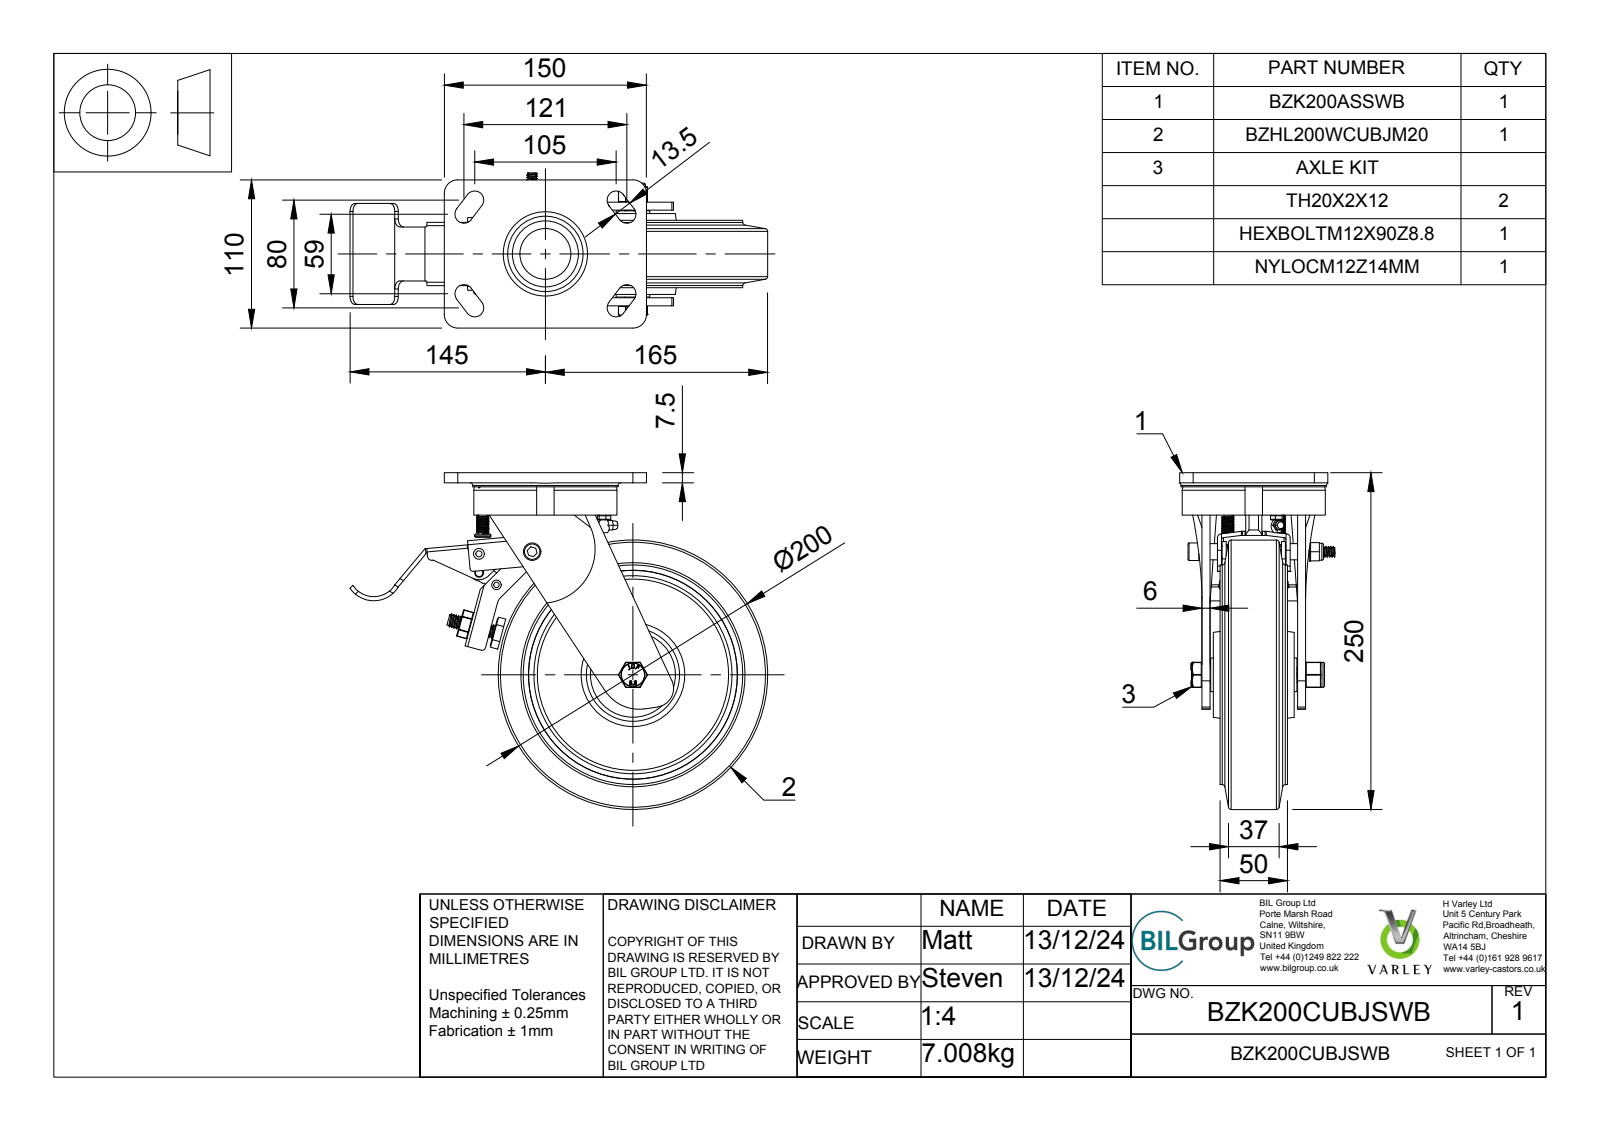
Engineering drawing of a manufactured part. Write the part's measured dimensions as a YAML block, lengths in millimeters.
part_name: "BZK200CUBJSWB v3; BZK200ASSWB v1; FABRICATED STEEL TOP PLATE; FABRICATED STEEL FORKS (+8 more)"
step_written_by: "Autodesk Translation Framework v13.20.0.188 (AP242_MANAGED_MODEL_BASED_3D_ENGINEERING_MIM_LF)"
units: millimeters
bodies: {solids: 56, faces: 1428, planar: 593, cylindrical: 366, other: 469}
overall_size: [310, 250, 115.22]
volume: 1364000
surface_area: 390820
round_holes:
  - {diameter: 6, count: 5}
  - {diameter: 10, count: 2}
  - {diameter: 5, count: 1}
  - {diameter: 8, count: 1}
  - {diameter: 12, count: 1}
  - {diameter: 12.2, count: 1}
  - {diameter: 13, count: 1}
  - {diameter: 14, count: 1}
  - {diameter: 20, count: 1}
  - {diameter: 28.5, count: 1}
  - {diameter: 30.8, count: 1}
  - {diameter: 37, count: 1}
round_bosses_or_shafts:
  - {diameter: 12, count: 3}
  - {diameter: 8, count: 2}
  - {diameter: 200, count: 1}
  - {diameter: 163, count: 1}
  - {diameter: 108, count: 1}
  - {diameter: 107, count: 1}
  - {diameter: 40.8, count: 1}
  - {diameter: 31.3, count: 1}
partial_cylinders:
  - {radius: 0.5, count: 50}
  - {radius: 1, count: 11}
  - {radius: 6, count: 8}
  - {radius: 6.75, count: 8}
  - {radius: 2.5, count: 5}
  - {radius: 10, count: 5}
  - {radius: 0.47, count: 4}
  - {radius: 0.9, count: 4}
face_to_face_distances: [7.5, 8, 36.5, 34.5, 71, 16.5, 42.5, 3, 6, 28.5]
hole_center_spacings: [50.23, 14.12, 15.62, 26.42, 36.19, 38, 39.54, 42.39]
